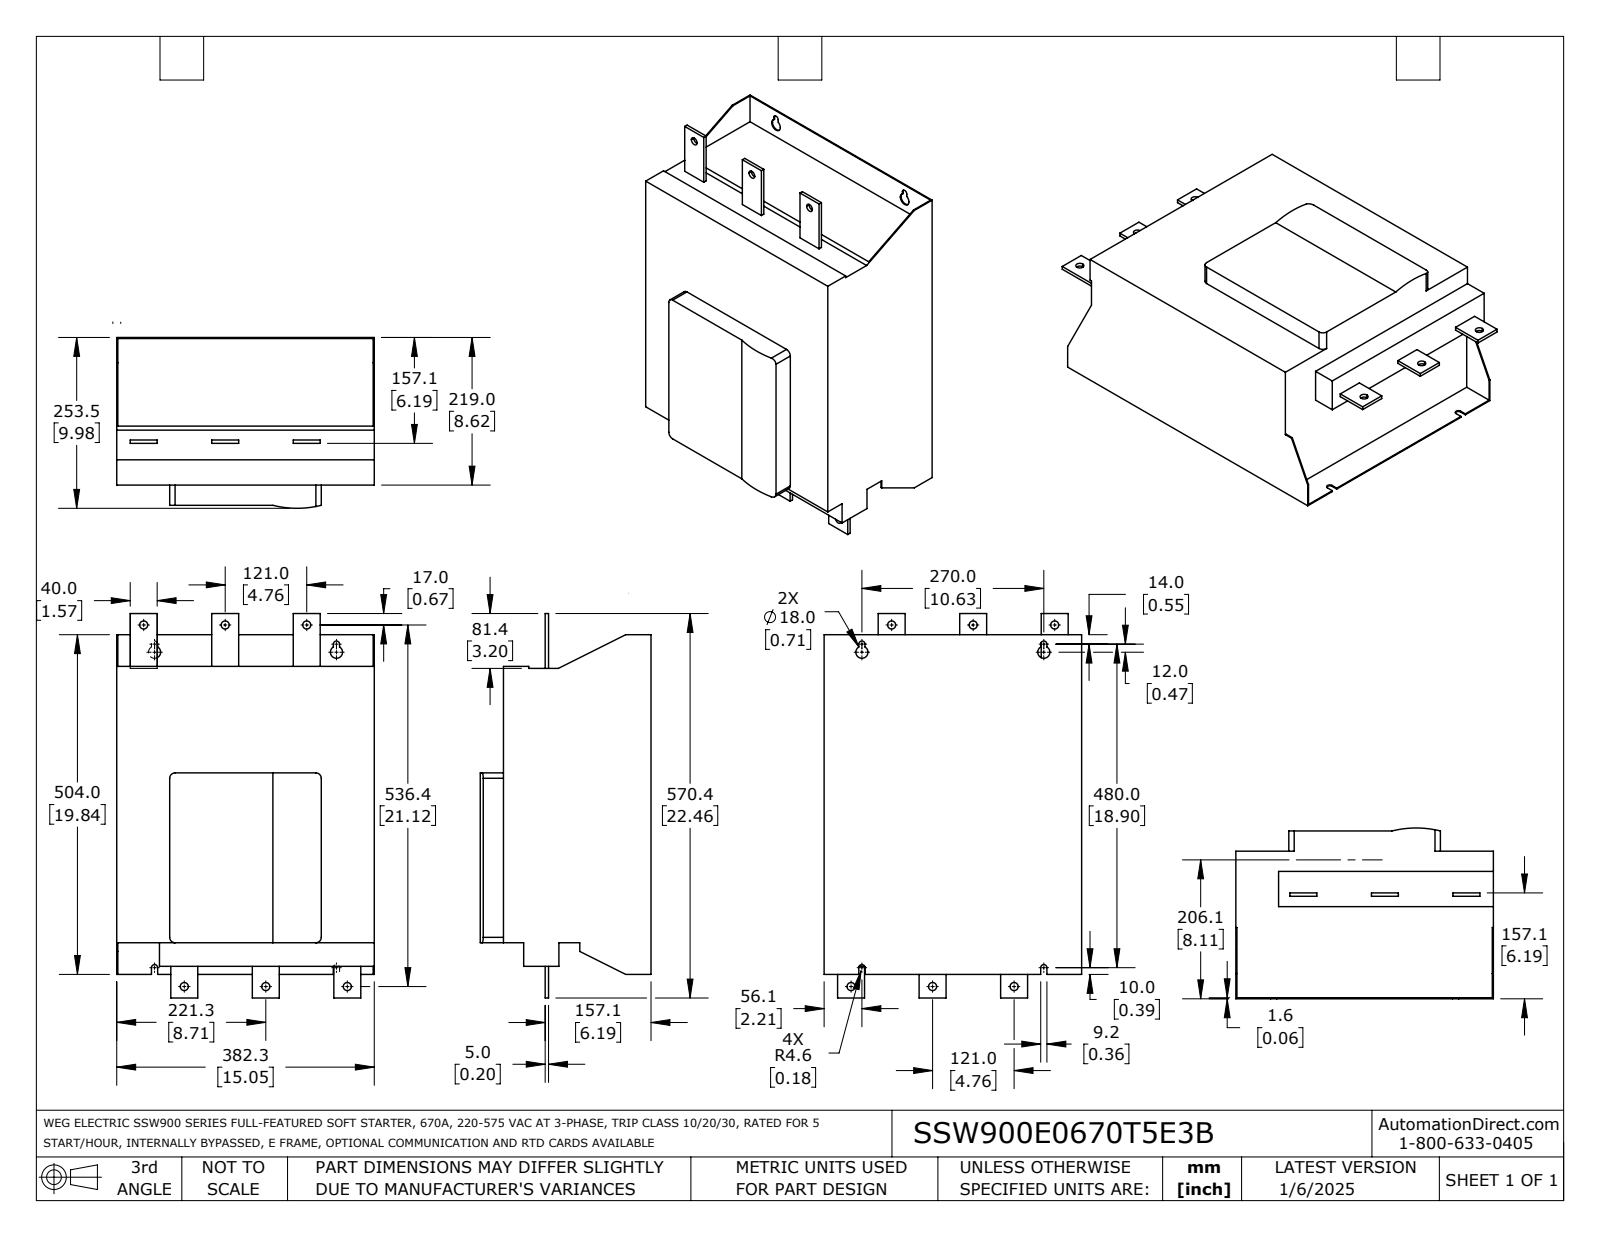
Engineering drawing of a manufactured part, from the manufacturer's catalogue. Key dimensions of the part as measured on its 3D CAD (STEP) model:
Part name (STEP PRODUCT): SSW900E0670T5E3B
STEP written by: SolidWorks 2021 (AUTOMOTIVE_DESIGN)
Units: inches
Bodies: 1 solid, 97 faces (70 planar, 27 cylindrical, 0 other)
Overall size (bounding box): 22.457 × 15.049 × 9.979
Volume: 2 243 in³ · Surface area: 1 320 in²
Round holes (diameter × count): ⌀0.472 ×6, ⌀0.709 ×2
Partial cylindrical surfaces — rounded edges, fillets, slot ends (radius × count): R0.181 ×4, R0.315 ×4, R5.788 ×1
Main face-to-face distances: 8.622, 15.049, 16.142, 0.063, 1.181, 9.803, 8.559, 9.74, 1.378, 16.024
Hole centre spacings: 4.764, 21.251, 9.528, 21.253, 22.291, 1.713, 2.356, 4.424
